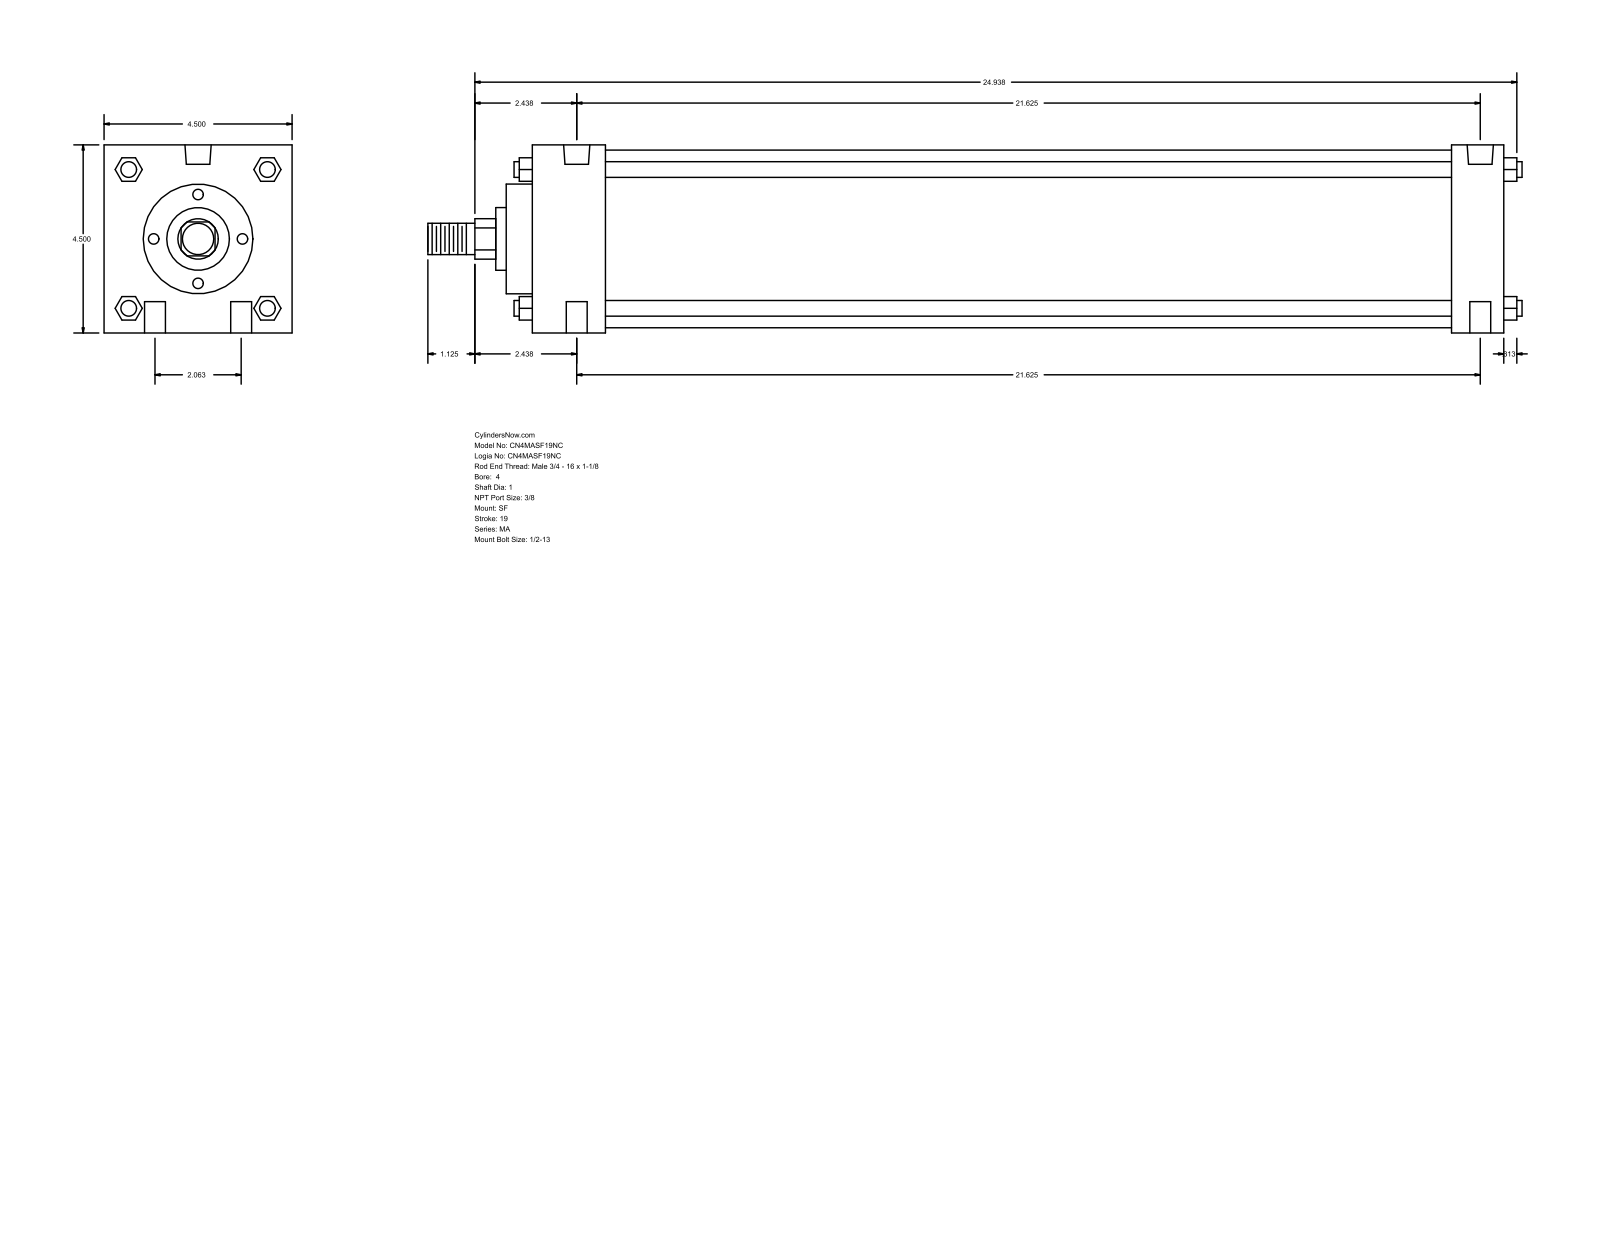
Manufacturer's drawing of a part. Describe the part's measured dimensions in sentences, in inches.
The part is named "MA_SF__0400_1". Its 3-D file was written by "GSSL Pune (CONFIG_CONTROL_DESIGN)". It is 0 solids with 126 faces: 95 planar, 31 cylindrical and 0 other. Overall it measures 26.187 by 4.5 by 4.5 inches. Round holes: 4 of diameter 0.5, 2 of diameter 0.437, 2 of diameter 0.627. Round bosses or shafts: 4 of diameter 0.375, 1 of diameter 4.25, 1 of diameter 2.625, 1 of diameter 1.5, 1 of diameter 1, 1 of diameter 0.75. Partial cylindrical surfaces (rounded edges, fillets, slot ends): 1 of radius 0.484. The main face-to-face distances are 4.5, 23.25, 22, 1.25, 1.75, 20.25, 21.5, 0.625, 2.375, 22.625. The hole center spacings are 1.031, 21.65, 21.625, 2.062, 21.723, 21.25.
